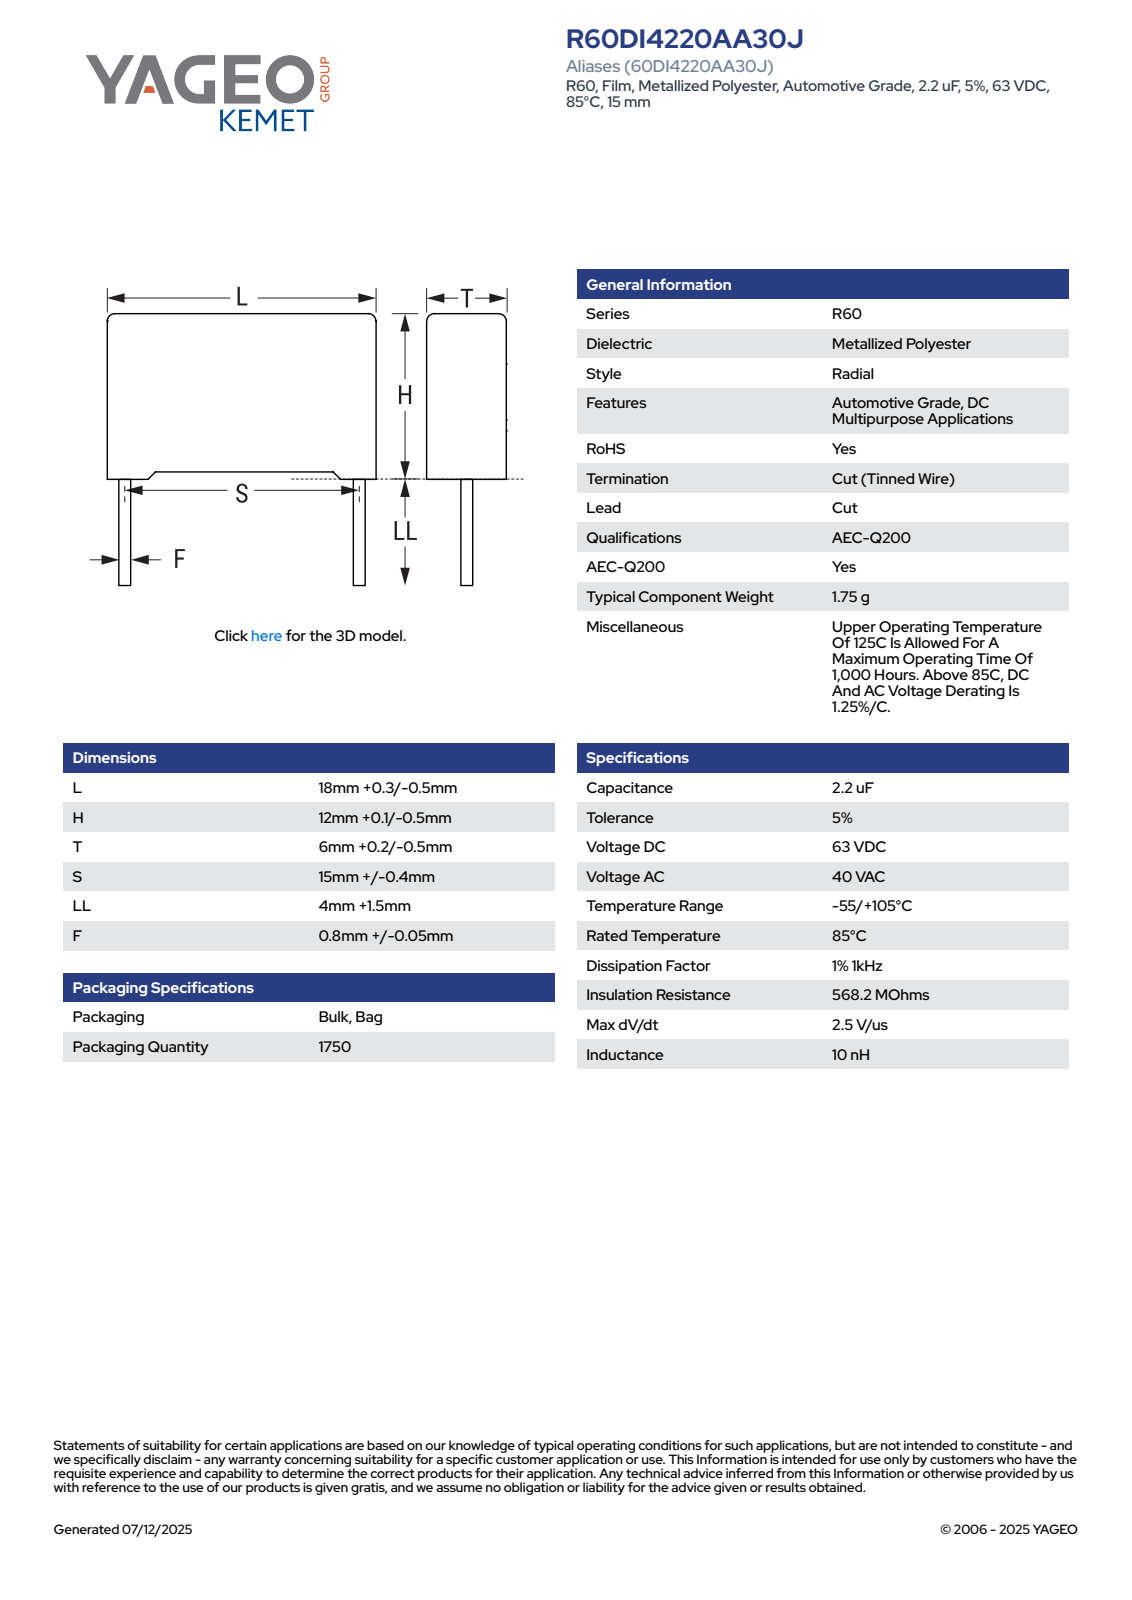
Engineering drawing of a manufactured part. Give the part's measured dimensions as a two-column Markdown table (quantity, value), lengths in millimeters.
| quantity | value |
| --- | --- |
| part name | CFR_RB2_18X12X6_L18.3H12.1T6.2S15LL5.5F0.85 |
| STEP written by | SolidWorks 2021 (AUTOMOTIVE_DESIGN) |
| units | millimeters |
| bodies | 4 solids, 85 faces (77 planar, 8 cylindrical, 0 other) |
| overall size | 18.3 × 17.6 × 6.21 |
| volume | 1 308 mm³ |
| surface area | 882 mm² |
| round bosses / shafts (diameter × count) | 0.85 × 2 |
| partial cylindrical surfaces (radius × count) | 0.5 × 4 |
| main face-to-face distances | 6.2, 11.35, 18.3, 0.61, 5.59, 0.75, 12.1, 0.42, 0.33, 11.68 |
